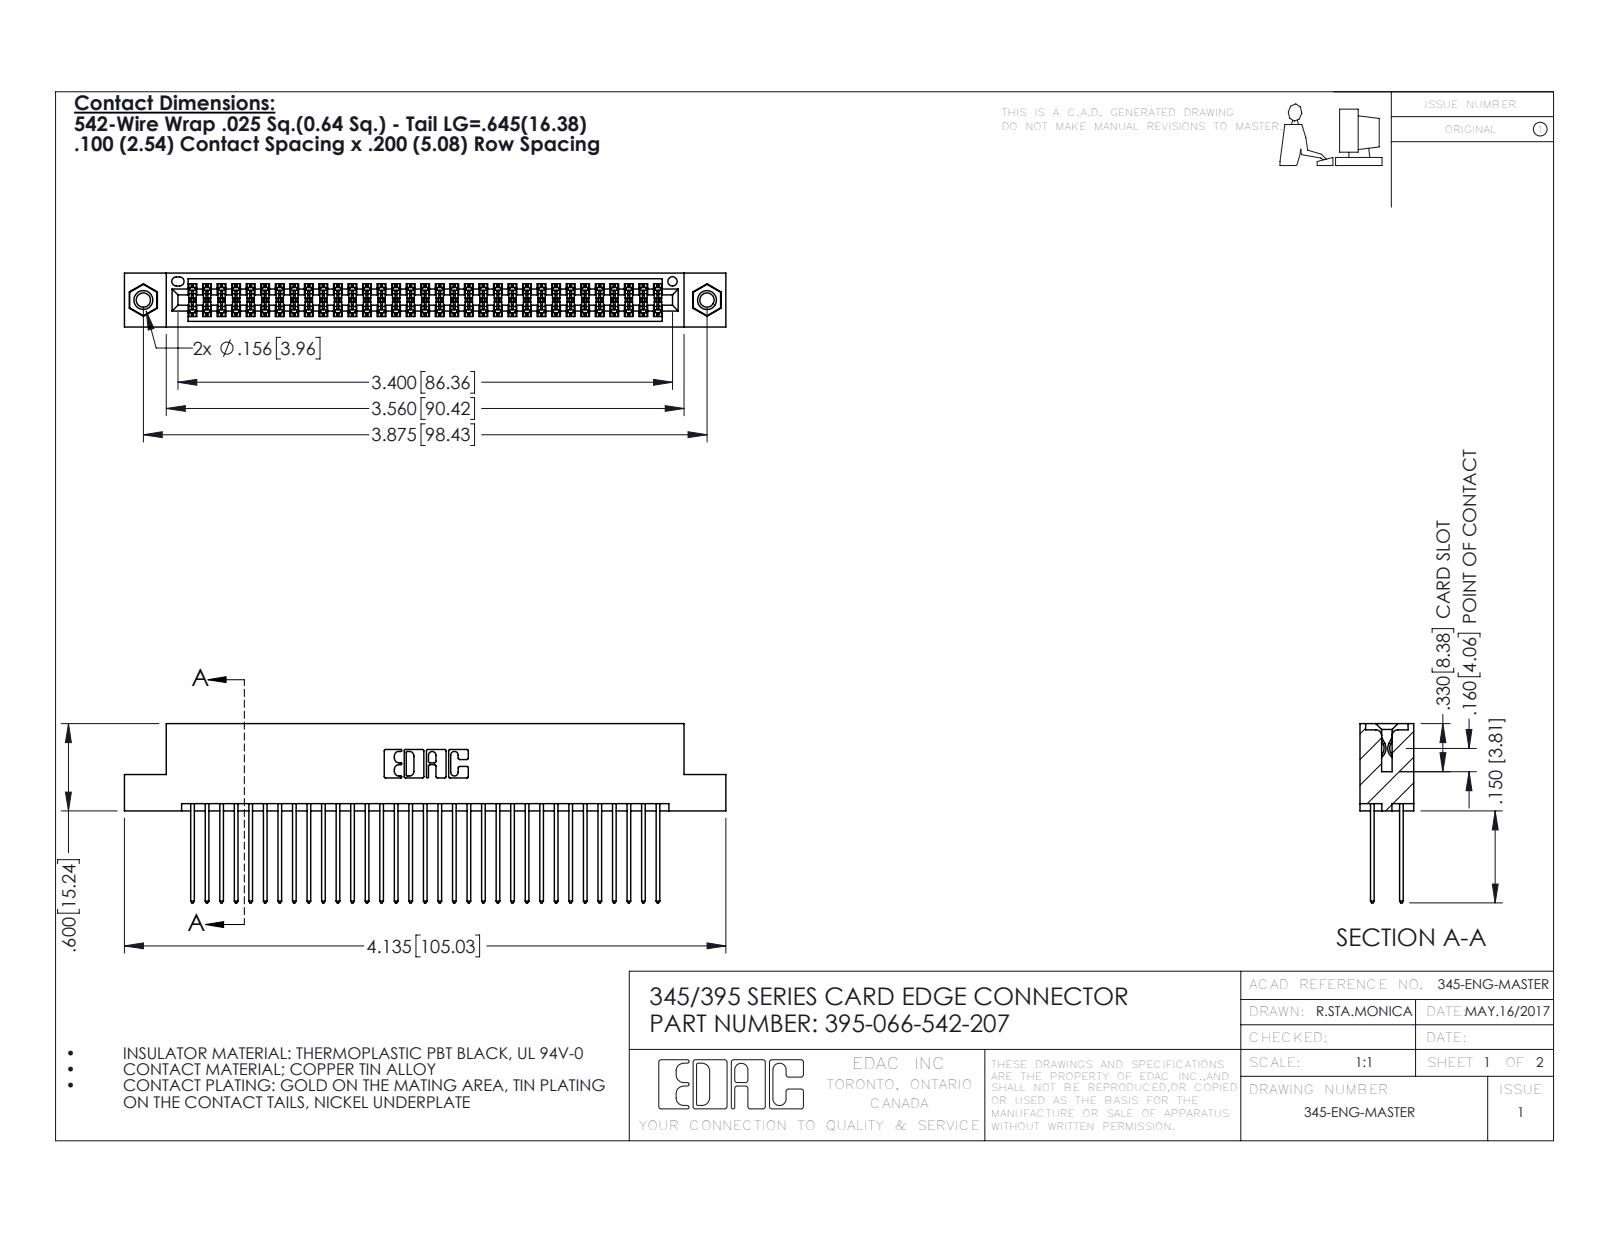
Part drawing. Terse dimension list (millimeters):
name: 345-250-001_345-250-005-103; 395-066-542-207; 345-292-001_345-293-142; 345 Part_Flush Mounting Lugs - 0.156 Dia-TI
written by: SolidWorks 2016 (CONFIG_CONTROL_DESIGN)
unit: mm
bodies: 69 solids, 3486 faces (2290 planar, 1180 cylindrical, 16 other)
size: 105 × 31.3 × 9.4
volume: 10 400 mm³; area: 16 680 mm²
holes: 2× ⌀2.5, 2× ⌀3.2, 2× ⌀4, 1× ⌀1.6
bosses: 2× ⌀3.9
rounds: 99× R0.2, 66× R0.3, 22× R0.3, 6× R0.2, 6× R0.8, 3× R0.7, 2× R0.4, 2× R0.5
face distances: 1.8, 7.6, 5.1, 2.5, 6.9, 0.6, 9.4, 5.7, 4.4, 3.8
hole spacings: 6.9, 92.5, 98.4
